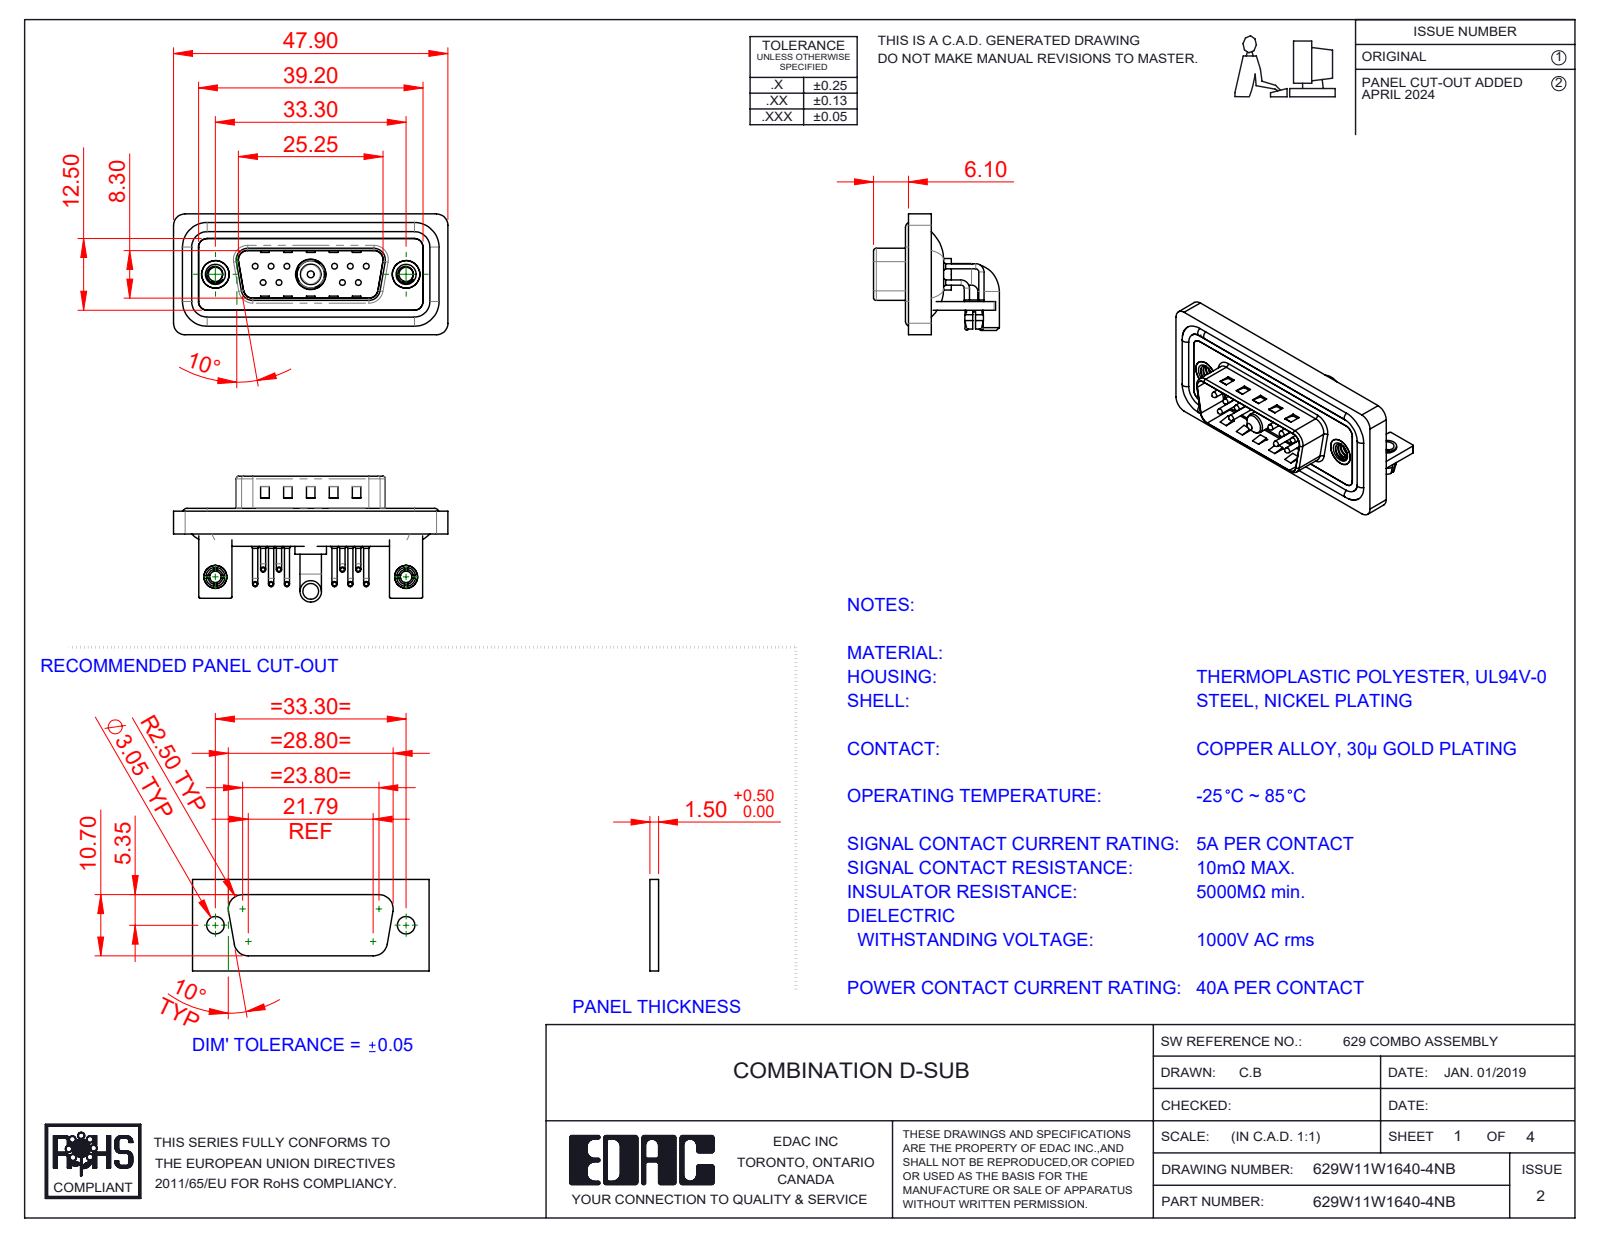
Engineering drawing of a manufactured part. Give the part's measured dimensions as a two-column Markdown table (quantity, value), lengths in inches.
| quantity | value |
| --- | --- |
| part name | 629Combo Contact Row 2; 629Combo Housing_11W1; 629Combo Shell Rear_15 Contacts; 629Combo Stabilizer Bracket (+7 more) |
| STEP written by | SolidWorks 2023 (CONFIG_CONTROL_DESIGN) |
| units | inches |
| bodies | 23 solids, 1733 faces (904 planar, 619 cylindrical, 210 other) |
| overall size | 1.886 × 0.865 × 0.831 |
| volume | 0.364 in³ |
| surface area | 15.69 in² |
| round holes (diameter × count) | 0.079 × 12, 0.03 × 10, 0.063 × 10, 0.098 × 4, 0.126 × 2, 0.157 × 2, 0.189 × 2, 0.197 × 2, 0.191 × 1, 0.209 × 1 |
| round bosses / shafts (diameter × count) | 0.035 × 20, 0.059 × 10, 0.039 × 10, 0.026 × 10, 0.063 × 4, 0.193 × 2, 0.157 × 2, 0.148 × 2 |
| partial cylindrical surfaces (radius × count) | 0.079 × 21, 0.059 × 18, 0.01 × 16, 0.04 × 10, 0.02 × 9, 0.063 × 8, 0.039 × 7, 0.024 × 4 |
| main face-to-face distances | 0.016, 0.031, 0.059, 0.114, 0.083, 0.043, 0.063, 0.047, 0.146, 0.161 |
| hole center spacings | 0.124, 0.109, 0.545, 0.436, 0.654, 0.198, 0.198, 0.218 |
